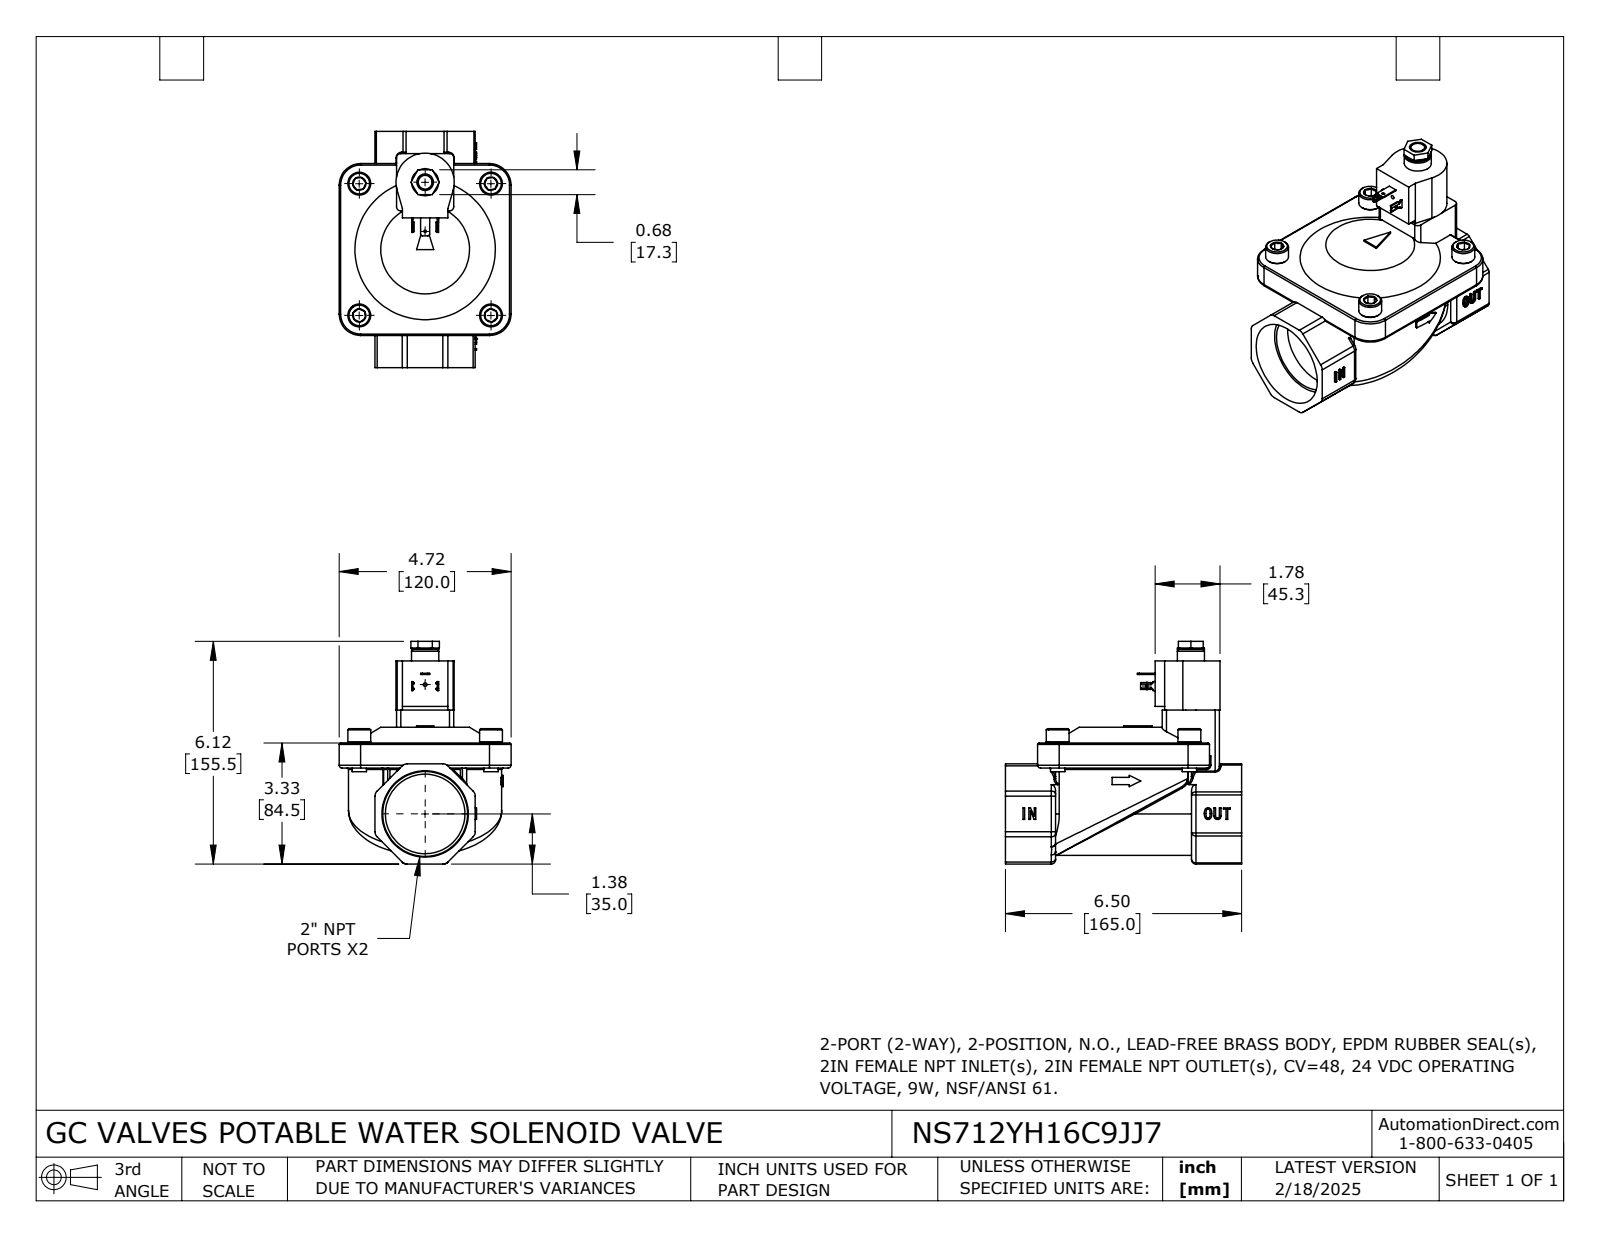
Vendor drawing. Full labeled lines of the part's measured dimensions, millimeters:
Part name (STEP PRODUCT): NS712YH16C9JJ7
STEP written by: SolidWorks 2024 (CONFIG_CONTROL_DESIGN)
Units: millimetres
Bodies: 1 solid, 478 faces (205 planar, 136 cylindrical, 137 other)
Overall size (bounding box): 165 × 155.51 × 120
Volume: 914 905 mm³ · Surface area: 96 823 mm²
Round holes (diameter × count): ⌀1.68 ×1, ⌀1.7 ×1, ⌀2.53 ×1, ⌀11.58 ×1, ⌀55.58 ×1
Round bosses / shafts (diameter × count): ⌀16 ×4, ⌀10 ×4, ⌀18.95 ×1
Partial cylindrical surfaces — rounded edges, fillets, slot ends (radius × count): R3 ×28, R1 ×21, R5 ×10, R0.15 ×4, R1.04 ×4, R2 ×4, R15 ×4, R1.27 ×2
Main face-to-face distances: 17.5, 69.99, 95, 11, 40, 28.5, 25, 70, 120, 142.5
Hole centre spacings: 34.29, 90.26
